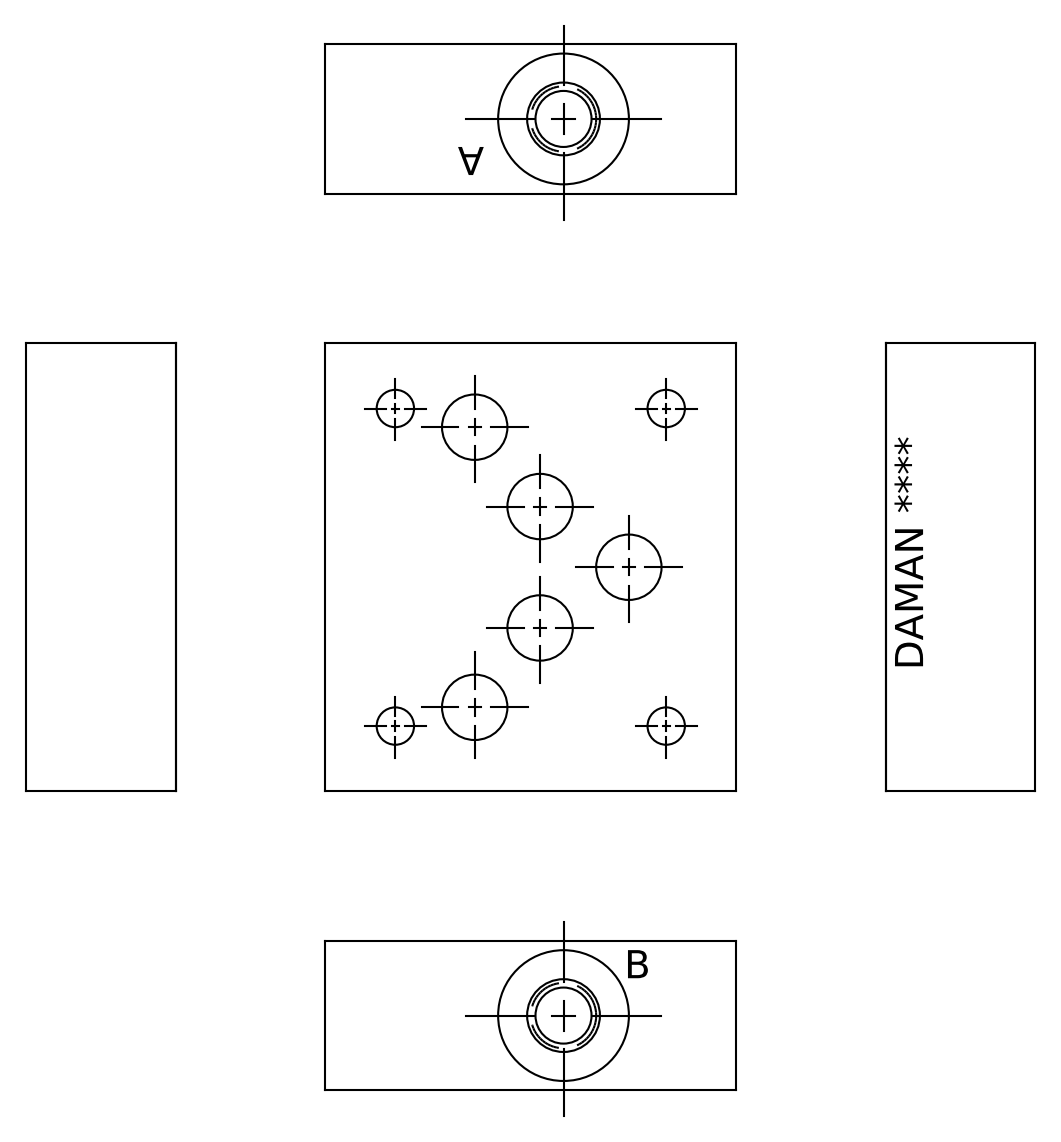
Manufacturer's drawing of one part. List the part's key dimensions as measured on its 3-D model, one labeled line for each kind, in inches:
Part name (STEP PRODUCT): Part_AD05TPAB4B.B01864R4_3D
STEP written by: Autodesk Inventor 2022 (AUTOMOTIVE_DESIGN)
Units: inches
Bodies: 1 solid, 427 faces (287 planar, 31 cylindrical, 109 other)
Overall size (bounding box): 3 × 2.75 × 1
Volume: 7.39 in³ · Surface area: 35.56 in²
Round holes (diameter × count): ⌀0.437 ×6, ⌀0.625 ×5, ⌀0.281 ×4, ⌀0.438 ×4, ⌀0.375 ×1, ⌀0.46 ×1, ⌀0.522 ×1, ⌀0.871 ×1
Partial cylindrical surfaces — rounded edges, fillets, slot ends (radius × count): R0.141 ×4
Main face-to-face distances: 1, 2.75, 3, 0.948, 0.052, 0.031, 2.969, 2.938, 2.748, 0.495
Hole centre spacings: 0.72, 1.394, 0.689, 1.412, 0.688, 0.72, 1.172, 0.688
